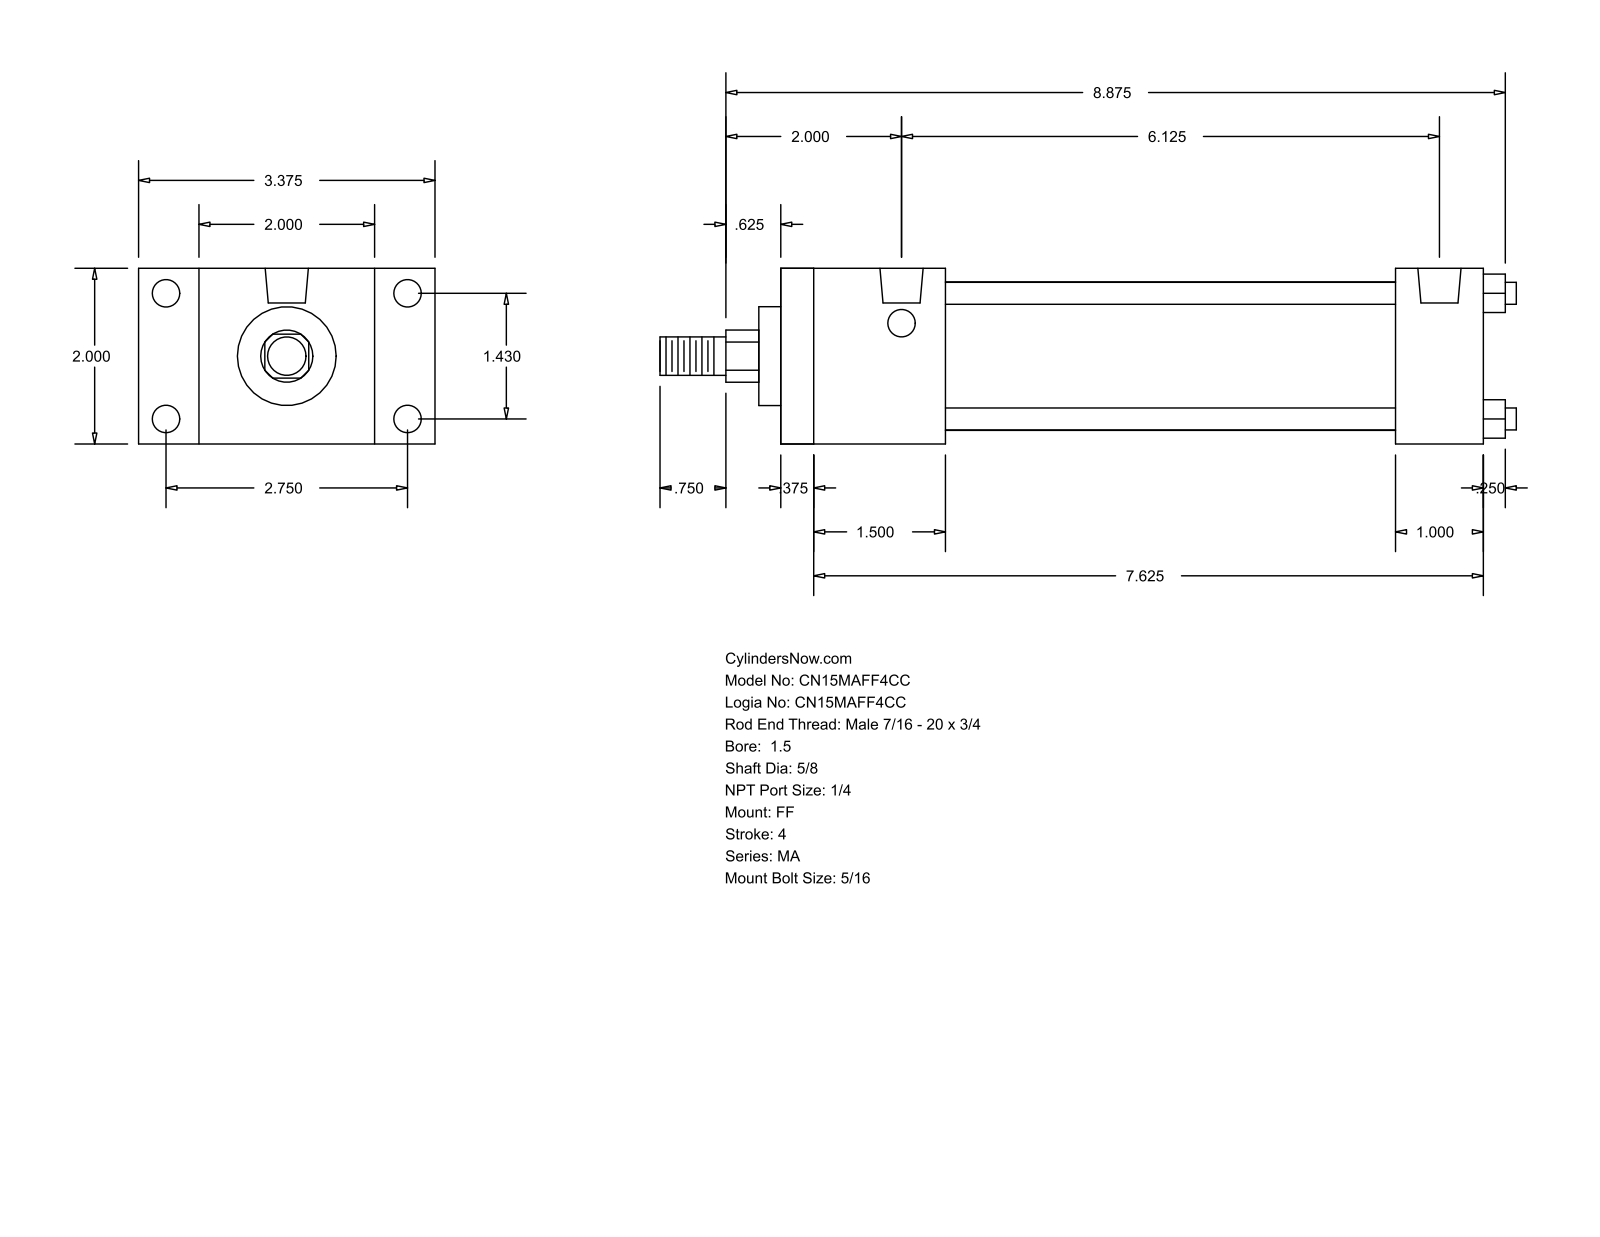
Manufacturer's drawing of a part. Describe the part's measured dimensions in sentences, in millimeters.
The part is named "MA_FF__0150_0.625". Its 3-D file was written by "GSSL Pune (CONFIG_CONTROL_DESIGN)". It is 0 solids with 92 faces: 64 planar, 28 cylindrical and 0 other. Overall it measures 247.65 by 85.72 by 50.8 millimeters. Round holes: 8 of diameter 7.94, 2 of diameter 12.49. Round bosses or shafts: 4 of diameter 6.35, 1 of diameter 42.93, 1 of diameter 28.57, 1 of diameter 15.88, 1 of diameter 11.11. Partial cylindrical surfaces (rounded edges, fillets, slot ends): 1 of radius 7.54. The main face-to-face distances are 50.8, 203.19, 9.52, 193.67, 47.62, 177.8, 38.1, 168.28, 130.18, 155.57. The hole center spacings are 36.32, 69.84, 78.72, 155.58.
